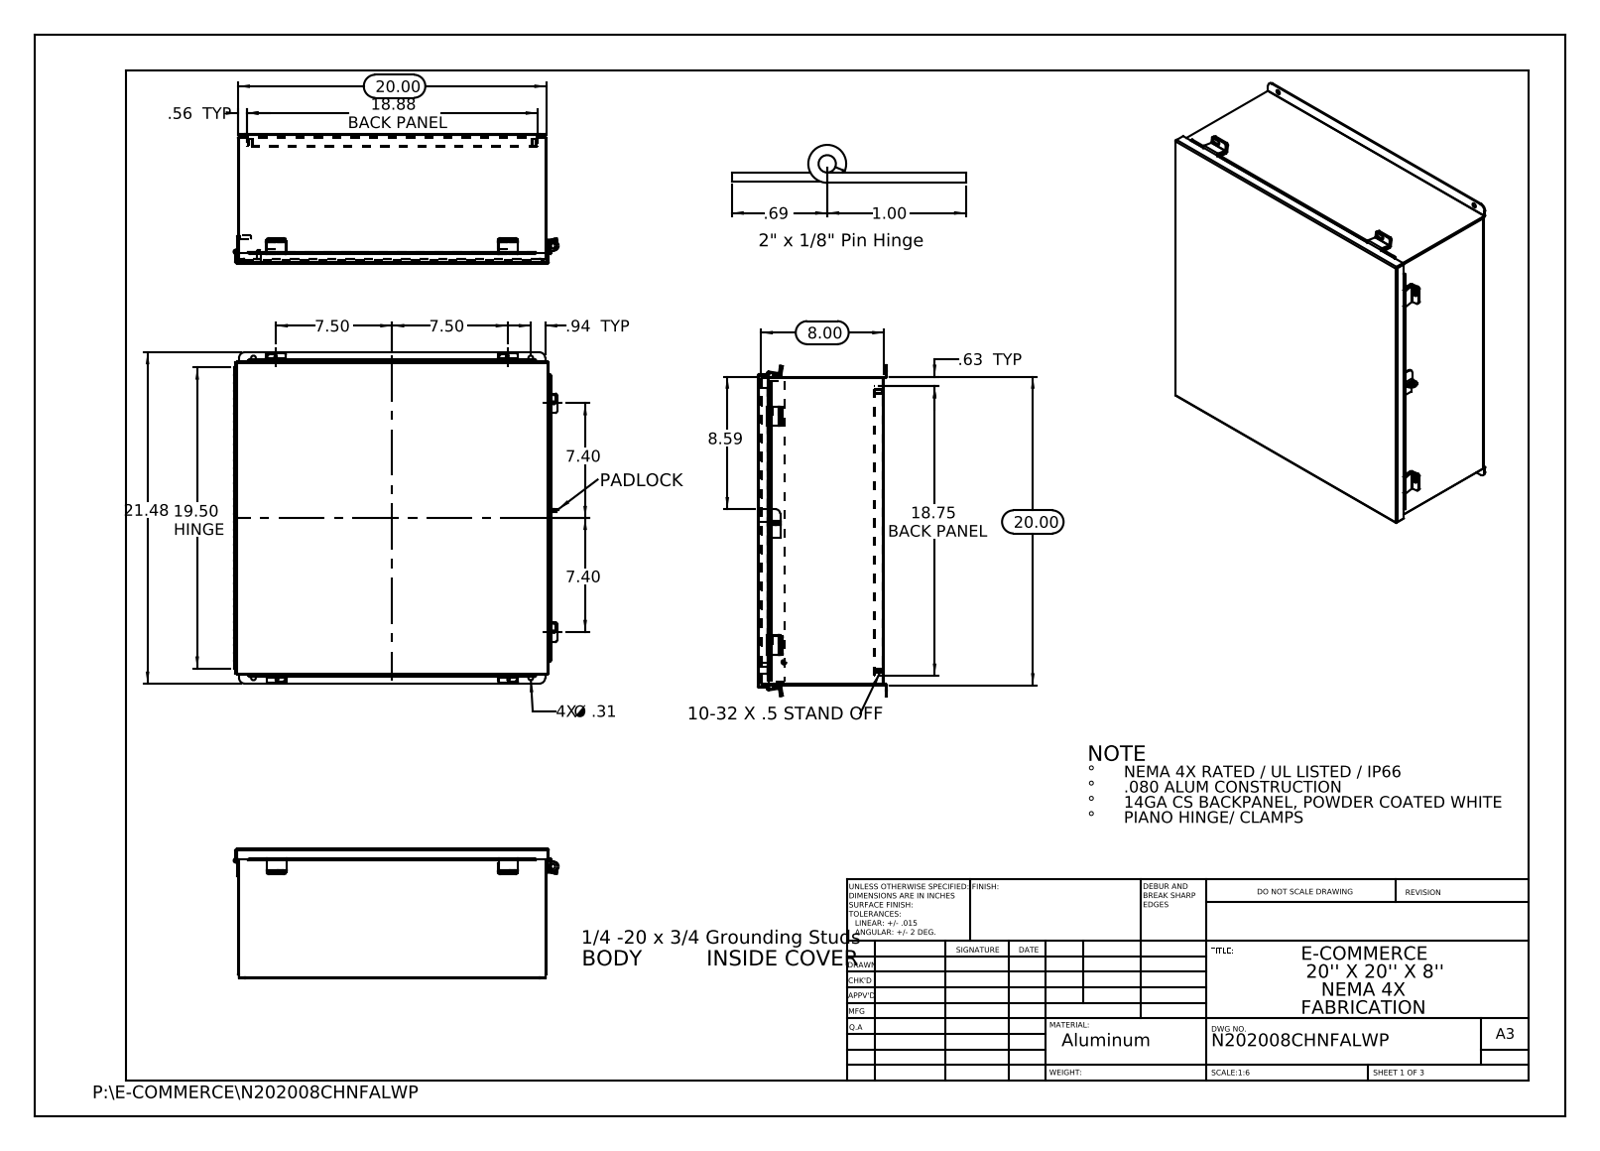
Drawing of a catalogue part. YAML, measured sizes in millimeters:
part_name: "N202008CHNFALWP Hinge Cover Side JIC; N202008CHNFALWP JIC_Cover_Template; N202008CHNFALWP JIC_Standoff; N202008CHNFALWP JIC Cover Clamp (+8 more)"
step_written_by: "SolidWorks 2013 (CONFIG_CONTROL_DESIGN)"
units: millimeters
bodies: {solids: 27, faces: 938, planar: 579, cylindrical: 339, other: 20}
overall_size: [545.5, 535.2, 213.1]
volume: 2412000
surface_area: 2572000
round_holes:
  - {diameter: 6.4, count: 10}
  - {diameter: 4.7, count: 4}
  - {diameter: 7.9, count: 4}
  - {diameter: 3.2, count: 1}
  - {diameter: 3.2, count: 1}
  - {diameter: 9.5, count: 1}
  - {diameter: 9.5, count: 1}
round_bosses_or_shafts:
  - {diameter: 8, count: 4}
  - {diameter: 8, count: 2}
  - {diameter: 6, count: 2}
  - {diameter: 6.9, count: 1}
  - {diameter: 6.4, count: 1}
partial_cylinders:
  - {radius: 3.2, count: 24}
  - {radius: 0.3, count: 13}
  - {radius: 0.2, count: 12}
  - {radius: 2.2, count: 12}
  - {radius: 3.4, count: 12}
  - {radius: 2.1, count: 6}
  - {radius: 2.5, count: 6}
  - {radius: 9.5, count: 4}
face_to_face_distances: [1.9, 206.5, 506.1, 204.5, 208.4, 193.8, 14.6, 12.7, 191.8, 16.5]
hole_center_spacings: [33.4, 462.8, 493.4, 675.7, 381, 456.6, 460.4, 466.7]
